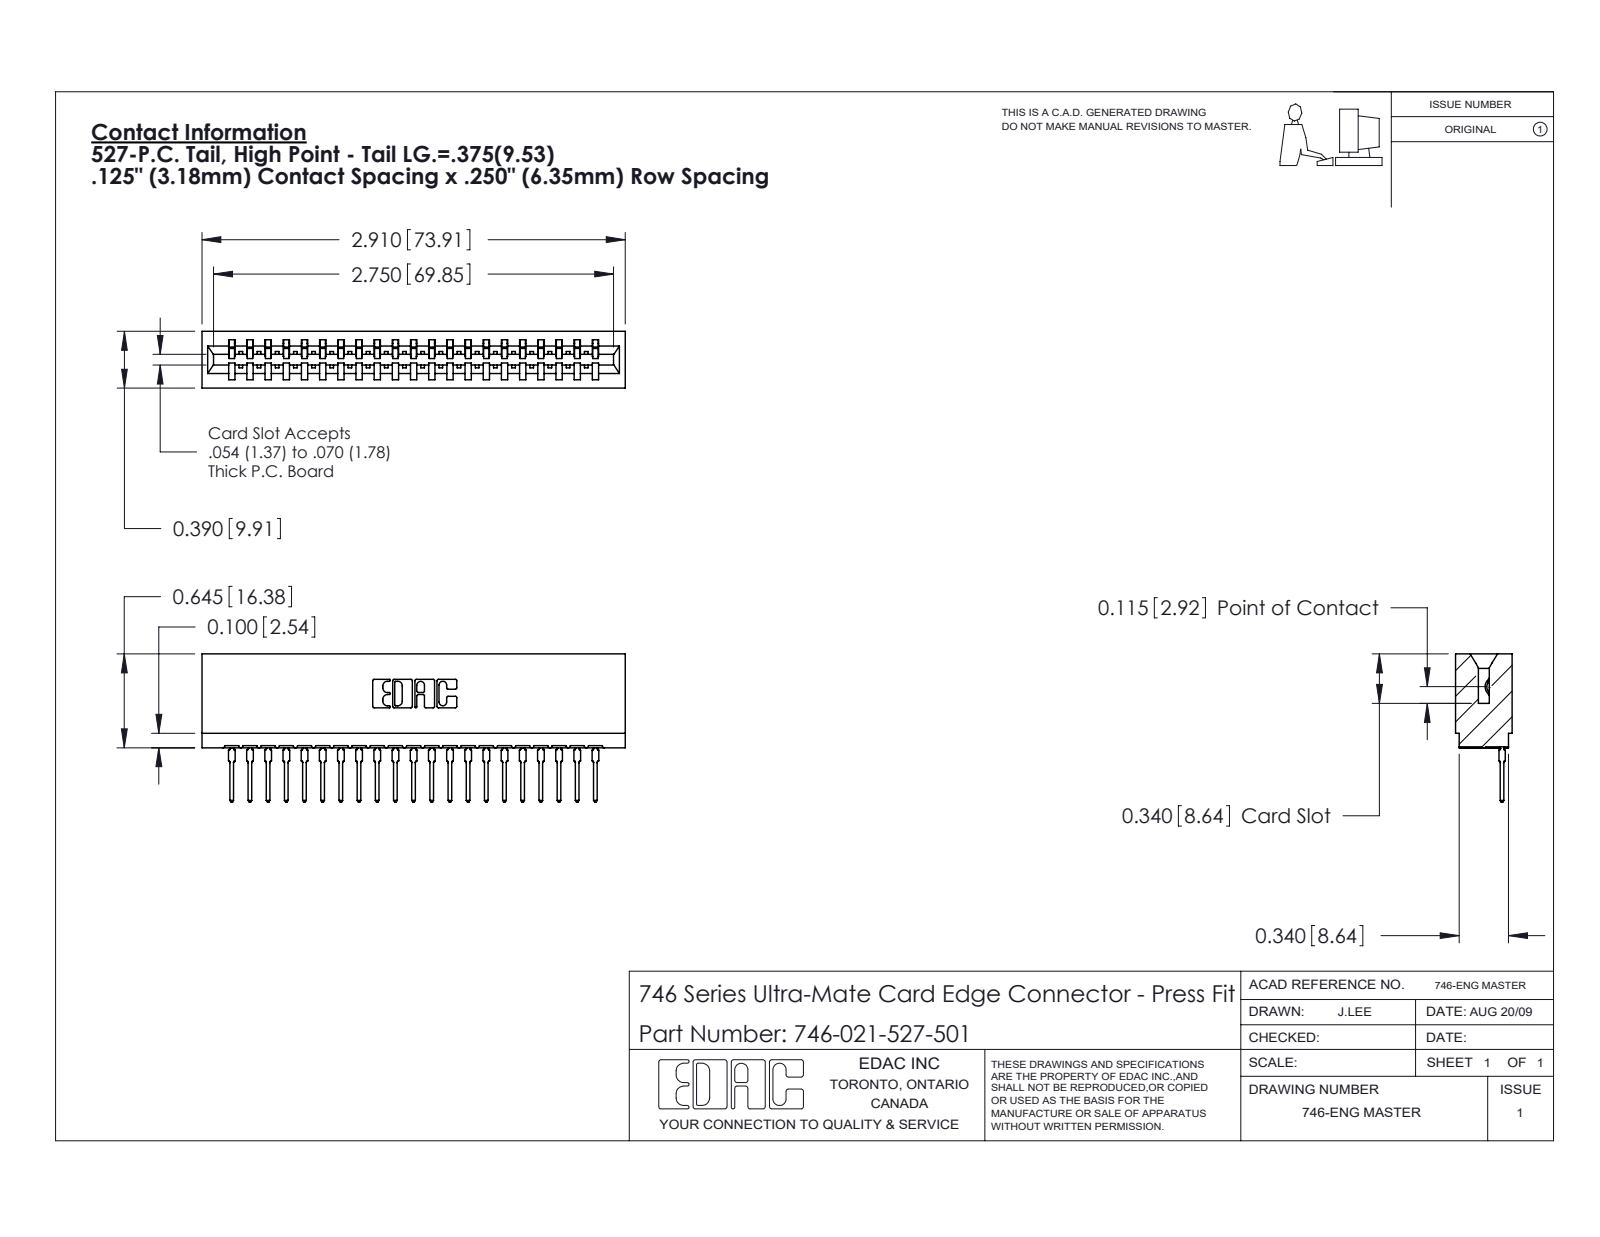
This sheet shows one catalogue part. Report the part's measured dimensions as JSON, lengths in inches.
{"part_name": "746-021-527-501; 746 Part_.340 Slot Depth - 01; 746-292-001_527", "step_written_by": "SolidWorks 2020 (CONFIG_CONTROL_DESIGN)", "units": "inches", "bodies": {"solids": 22, "faces": 2365, "planar": 1378, "cylindrical": 441, "other": 546}, "overall_size": [2.91, 1.019, 0.39], "volume_in3": 0.515, "surface_area_in2": 17.34, "partial_cylinders_radius": [[0.021, 42], [0.01, 22], [0.015, 22], [0.007, 6], [0.031, 6], [0.005, 4], [0.011, 4], [0.026, 3]], "face_to_face_distances": [0.25, 0.057, 0.333, 0.39, 0.5, 0.125, 0.292, 0.125, 0.025, 0.307]}
